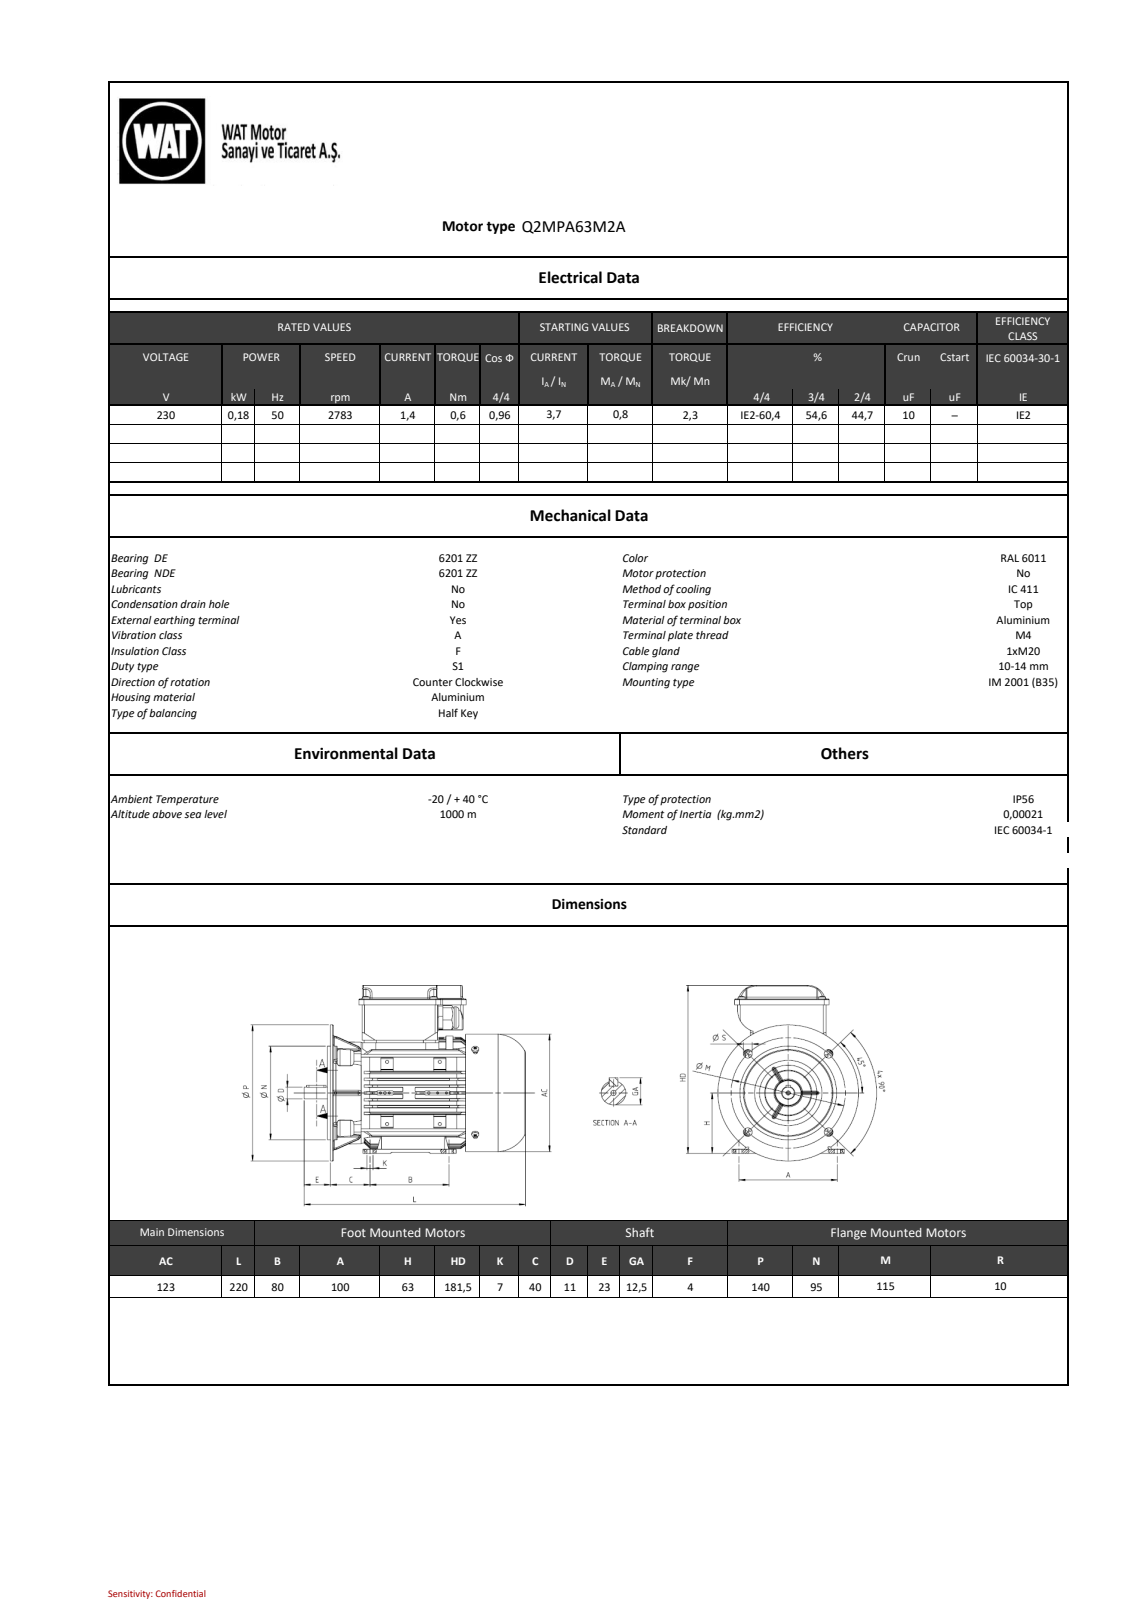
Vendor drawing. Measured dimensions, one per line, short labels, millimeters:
name: BY6434017xx_004-TK_QM63-80; BY6424130xx_004-TKK_QM63-80; BY6434010xx_005-MOTOR_KAPAGI_QS63_FA_ISLEME; BY6423003xx_006-FAN_KAPAGI_QS63 (+8 more)
written by: SIEMENS PLM Software NX2206.8101 (AUTOMOTIVE_DESIGN)
unit: mm
bodies: 36 solids, 2377 faces (1208 planar, 809 cylindrical, 360 other)
size: 219.47 × 188.6 × 140.2
volume: 660 220 mm³; area: 437 178 mm²
holes: 10× ⌀3.65, 8× ⌀4.5, 8× ⌀10, 6× ⌀2.5, 5× ⌀3.3, 4× ⌀3.5, 4× ⌀4, 4× ⌀4.2, 4× ⌀4.65, 4× ⌀4.8, 3× ⌀3, 2× ⌀7
bosses: 8× ⌀8, 8× ⌀4, 8× ⌀3, 1× ⌀140.2, 1× ⌀123, 1× ⌀95, 1× ⌀70, 1× ⌀30
rounds: 212× R0.5, 126× R1, 68× R2, 20× R2.5, 11× R5, 9× R3, 9× R5.5, 8× R1.5
face distances: 3, 1, 2.5, 4, 7.02, 27.96, 4.5, 10.5, 1.5, 7
hole spacings: 42.93, 103.43, 55, 44.01, 54, 57.5, 79.19, 81.32
